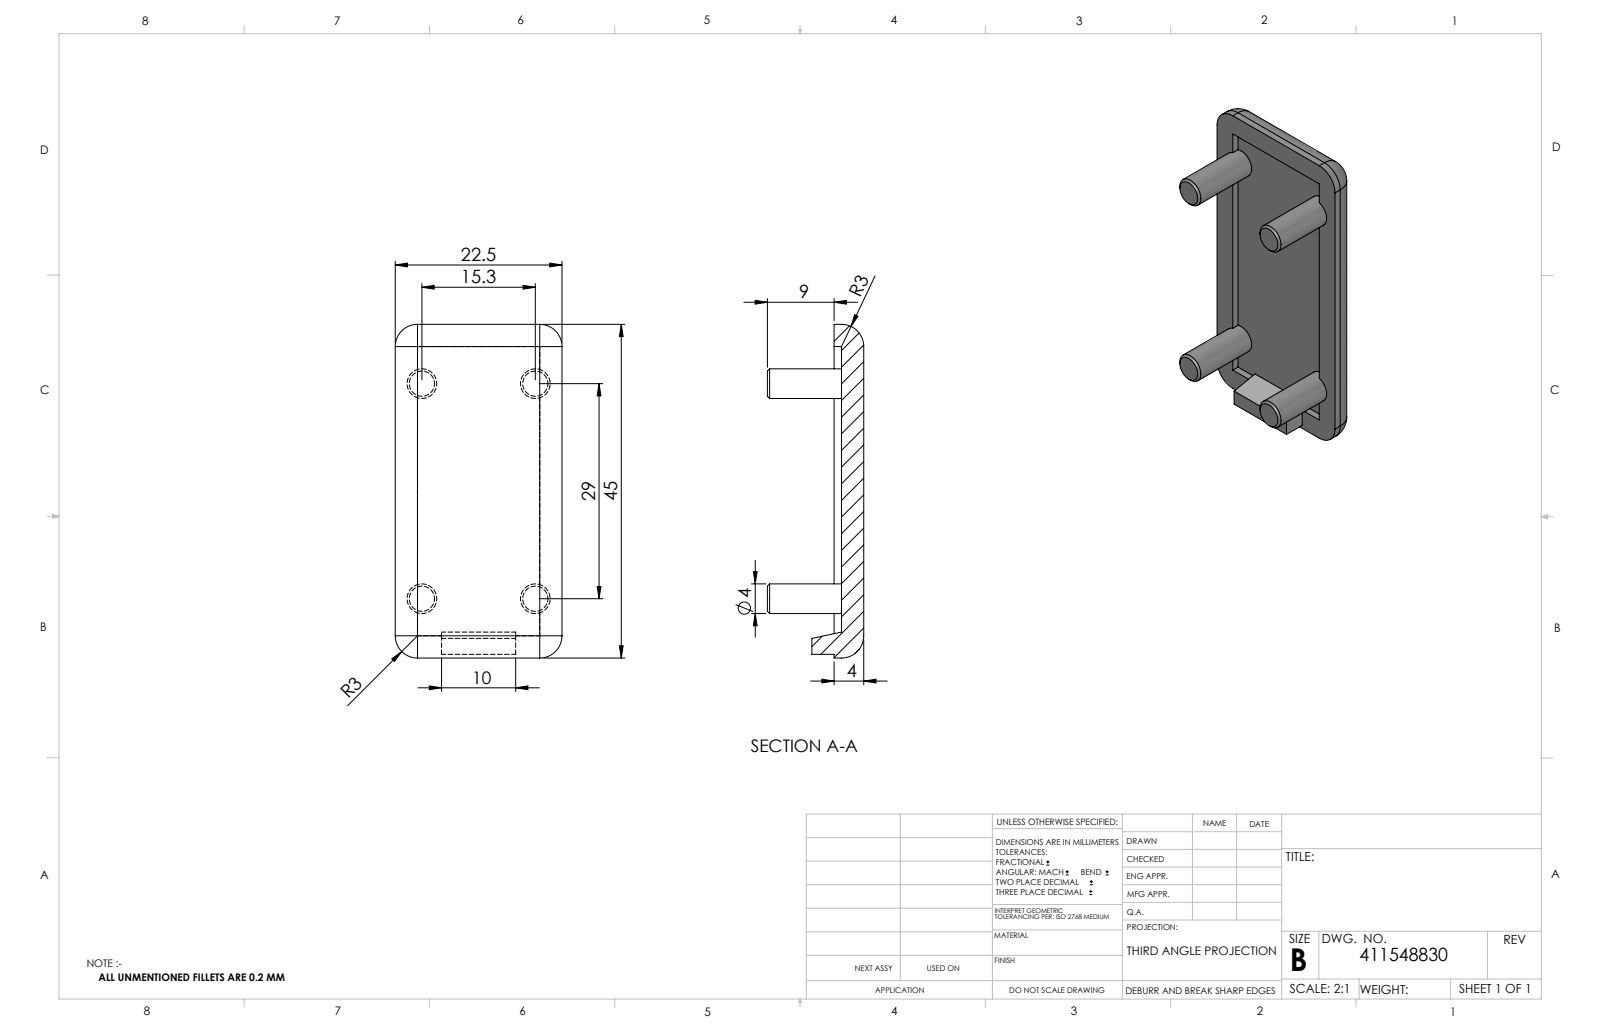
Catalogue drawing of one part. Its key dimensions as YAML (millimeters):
part_name: "411548830"
step_written_by: "SolidWorks 2014 (CONFIG_CONTROL_DESIGN)"
units: millimeters
bodies: {solids: 1, faces: 53, planar: 25, cylindrical: 16, other: 12}
overall_size: [45, 22.5, 13]
volume: 3696
surface_area: 2995
round_bosses_or_shafts:
  - {diameter: 4, count: 4}
partial_cylinders:
  - {radius: 3, count: 8}
face_to_face_distances: [3, 4, 1, 19.5, 10, 22.5, 9, 13, 16.5, 42]
